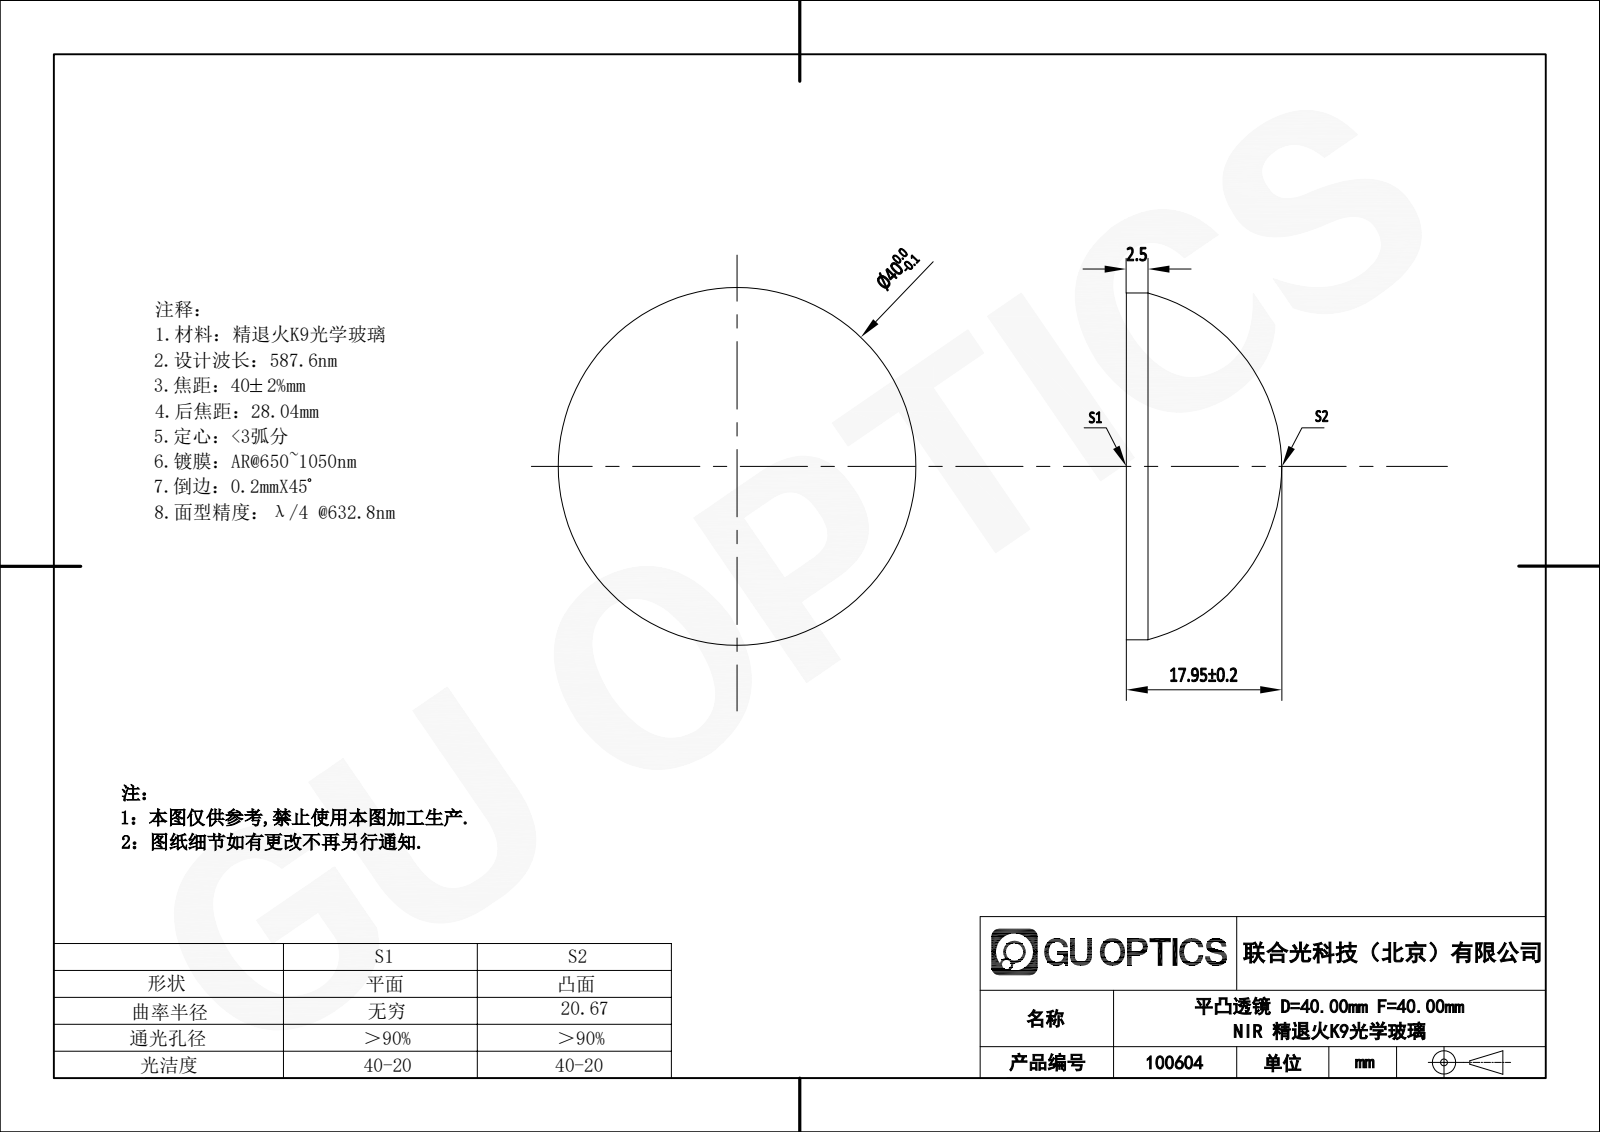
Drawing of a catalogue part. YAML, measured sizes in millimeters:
part_name: "100604"
step_written_by: "SolidWorks 2020 (CONFIG_CONTROL_DESIGN)"
units: millimeters
bodies: {solids: 1, faces: 5, planar: 1, cylindrical: 2, other: 2}
overall_size: [40, 40, 17.95]
volume: 14780
surface_area: 3577
round_bosses_or_shafts:
  - {diameter: 40, count: 1}
